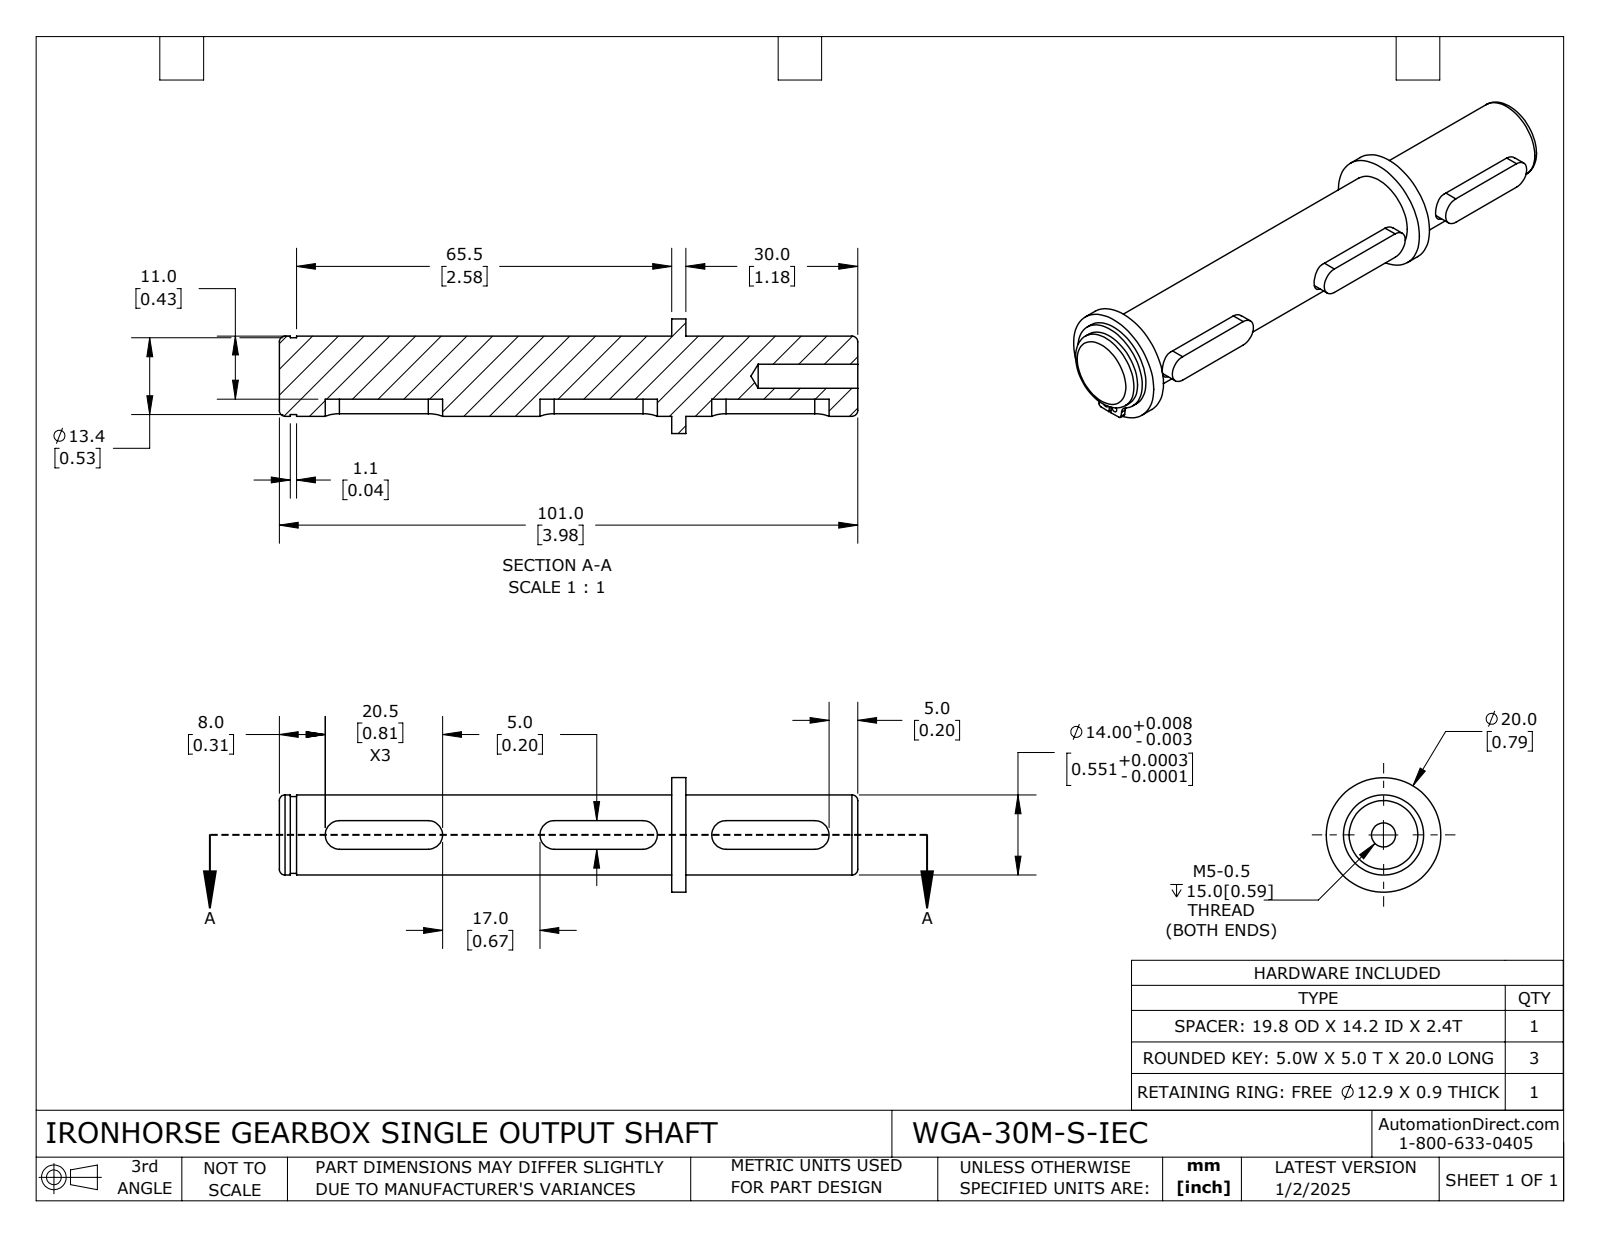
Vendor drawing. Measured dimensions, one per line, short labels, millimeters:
name: WGA-30M-S-IEC
written by: SolidWorks 2024 (CONFIG_CONTROL_DESIGN)
unit: mm
bodies: 6 solids, 91 faces (37 planar, 48 cylindrical, 6 other)
size: 101 × 20 × 20
volume: 16 677 mm³; area: 7 738 mm²
holes: 2× ⌀1.2, 1× ⌀4.2, 1× ⌀13.25, 1× ⌀14.2
bosses: 1× ⌀20, 1× ⌀19.8, 1× ⌀15.9, 1× ⌀14, 1× ⌀13.4
rounds: 9× R2.5, 2× R0.5, 2× R1.8
face distances: 5, 68, 65.5, 2.5, 2.4, 63.1, 65.6, 3, 5.4, 68.5
hole spacings: 8.22, 2.1
